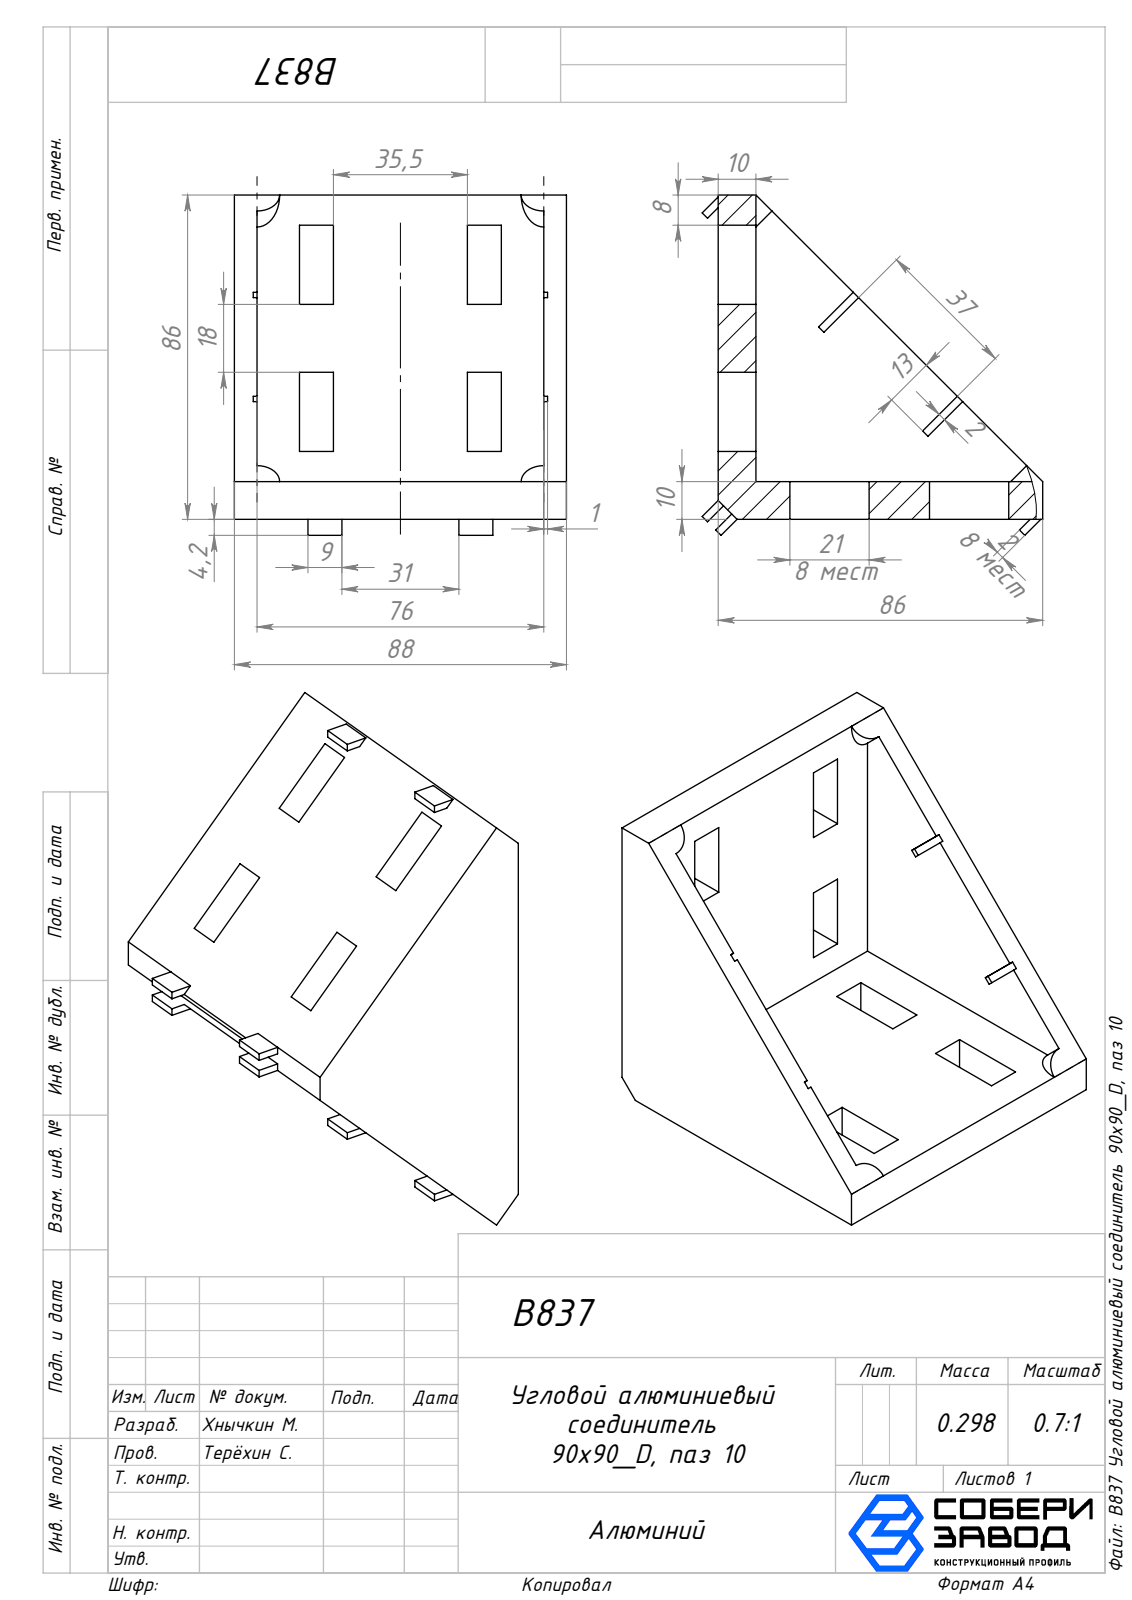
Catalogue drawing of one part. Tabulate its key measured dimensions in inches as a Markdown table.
| quantity | value |
| --- | --- |
| part name | B837 Угловой алюминиевый соединитель 90х90_D, паз 10 |
| STEP written by | SolidWorks 2025 (AUTOMOTIVE_DESIGN) |
| units | inches |
| bodies | 1 solid, 103 faces (99 planar, 4 cylindrical, 0 other) |
| overall size | 3.553 × 3.553 × 3.465 |
| volume | 9.892 in³ |
| surface area | 73.25 in² |
| partial cylindrical surfaces (radius × count) | 0.236 × 4 |
| main face-to-face distances | 0.394, 0.236, 3.228, 2.992, 3.465, 0.354, 3.386, 1.742, 0.443, 0.689 |
